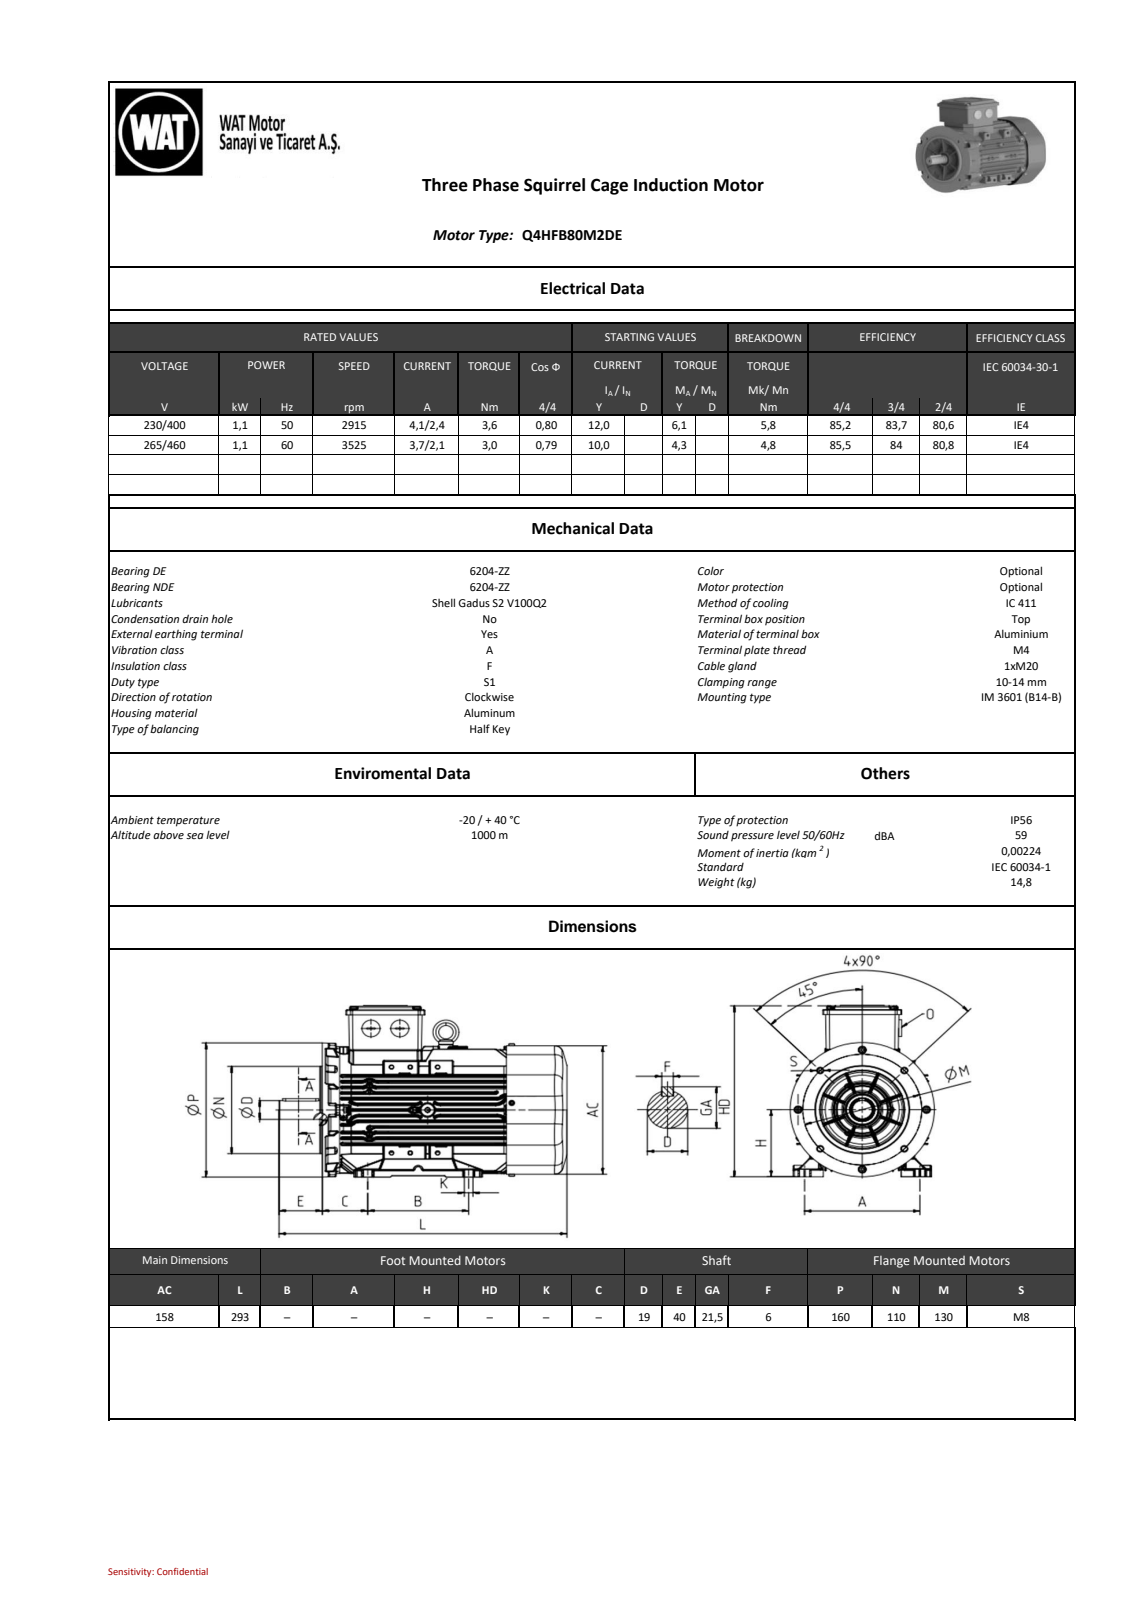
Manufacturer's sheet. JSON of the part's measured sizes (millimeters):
{"part_name": "model1", "step_written_by": "SIEMENS PLM Software NX2206.8101 (AUTOMOTIVE_DESIGN)", "units": "millimeters", "bodies": {"solids": 0, "faces": 5645, "planar": 1094, "cylindrical": 1597, "other": 2954}, "overall_size": [293, 215.5, 160], "round_holes": [[3, 2], [3.5, 2], [4.6, 2], [5, 1], [8, 1], [51, 1], [57, 1]], "round_bosses_or_shafts": [[6, 6], [21.38, 2], [8.33, 2], [146.5, 1], [110, 1], [61, 1], [30, 1], [24.07, 1]], "partial_cylinders_radius": [[0.5, 525], [0.8, 281], [1, 223], [2, 41], [1.5, 16], [5, 12], [75.75, 8], [2.25, 4]], "face_to_face_distances": [1, 41.96, 157, 156.98, 10.36, 86, 10.49, 52.32, 221, 18], "hole_center_spacings": [25.5, 44.17, 70.94]}
